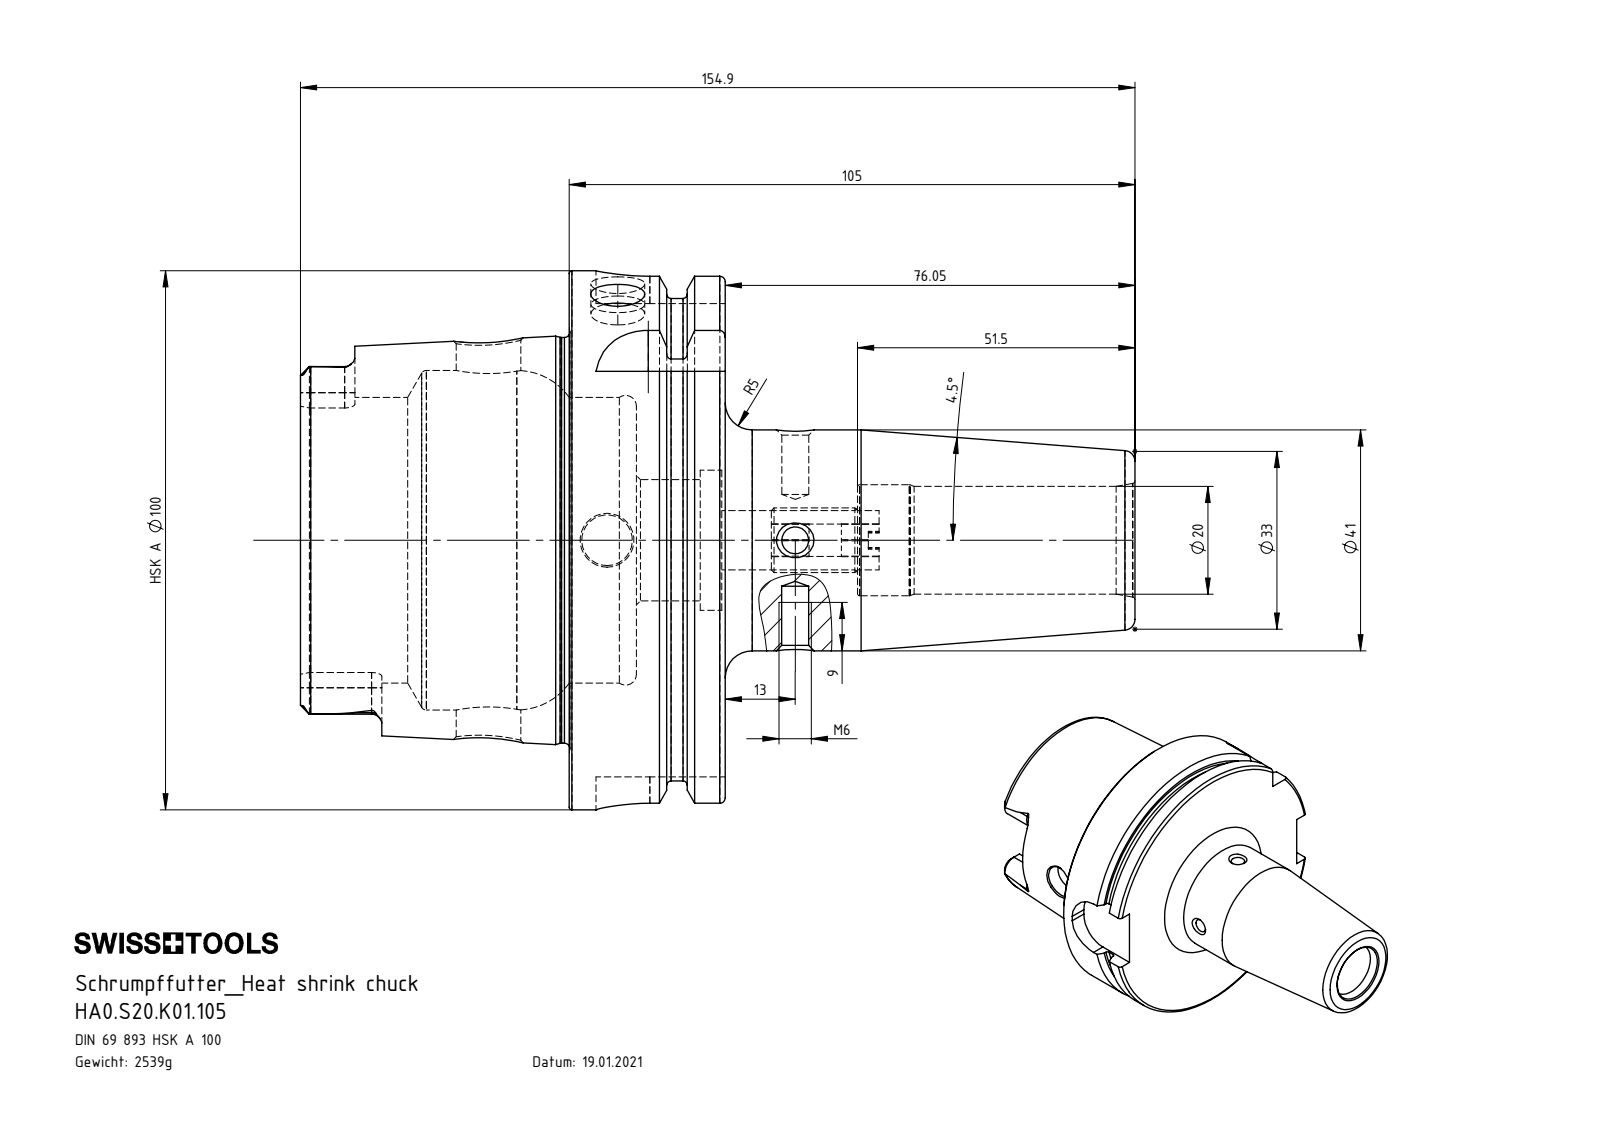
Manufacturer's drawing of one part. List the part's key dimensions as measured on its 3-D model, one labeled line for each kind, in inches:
Part name (STEP PRODUCT): HA0.S20.K01.105; ERU-AN5.K01.020_A; HA0-S20.K01.105_B_Fertigbearbeitung
STEP written by: SolidWorks 2017 (CONFIG_CONTROL_DESIGN)
Units: inches
Bodies: 2 solids, 240 faces (74 planar, 64 cylindrical, 102 other)
Overall size (bounding box): 6.098 × 3.937 × 3.937
Volume: 19.77 in³ · Surface area: 99.07 in²
Round holes (diameter × count): ⌀0.197 ×2, ⌀0.236 ×1, ⌀0.394 ×1, ⌀0.433 ×1, ⌀0.472 ×1, ⌀0.787 ×1, ⌀0.811 ×1, ⌀0.886 ×1, ⌀1.024 ×1, ⌀2.087 ×1, ⌀2.48 ×1
Round bosses / shafts (diameter × count): ⌀3.937 ×1, ⌀3.62 ×1, ⌀2.963 ×1, ⌀1.614 ×1, ⌀0.472 ×1
Partial cylindrical surfaces — rounded edges, fillets, slot ends (radius × count): R0.075 ×6, R0.192 ×4, R0.394 ×4
Main face-to-face distances: 1.14, 0.49, 0.65, 1.965, 2.455, 3.104, 3.457, 3.079, 1.114, 0.624
Hole centre spacings: 1.376, 2.242
